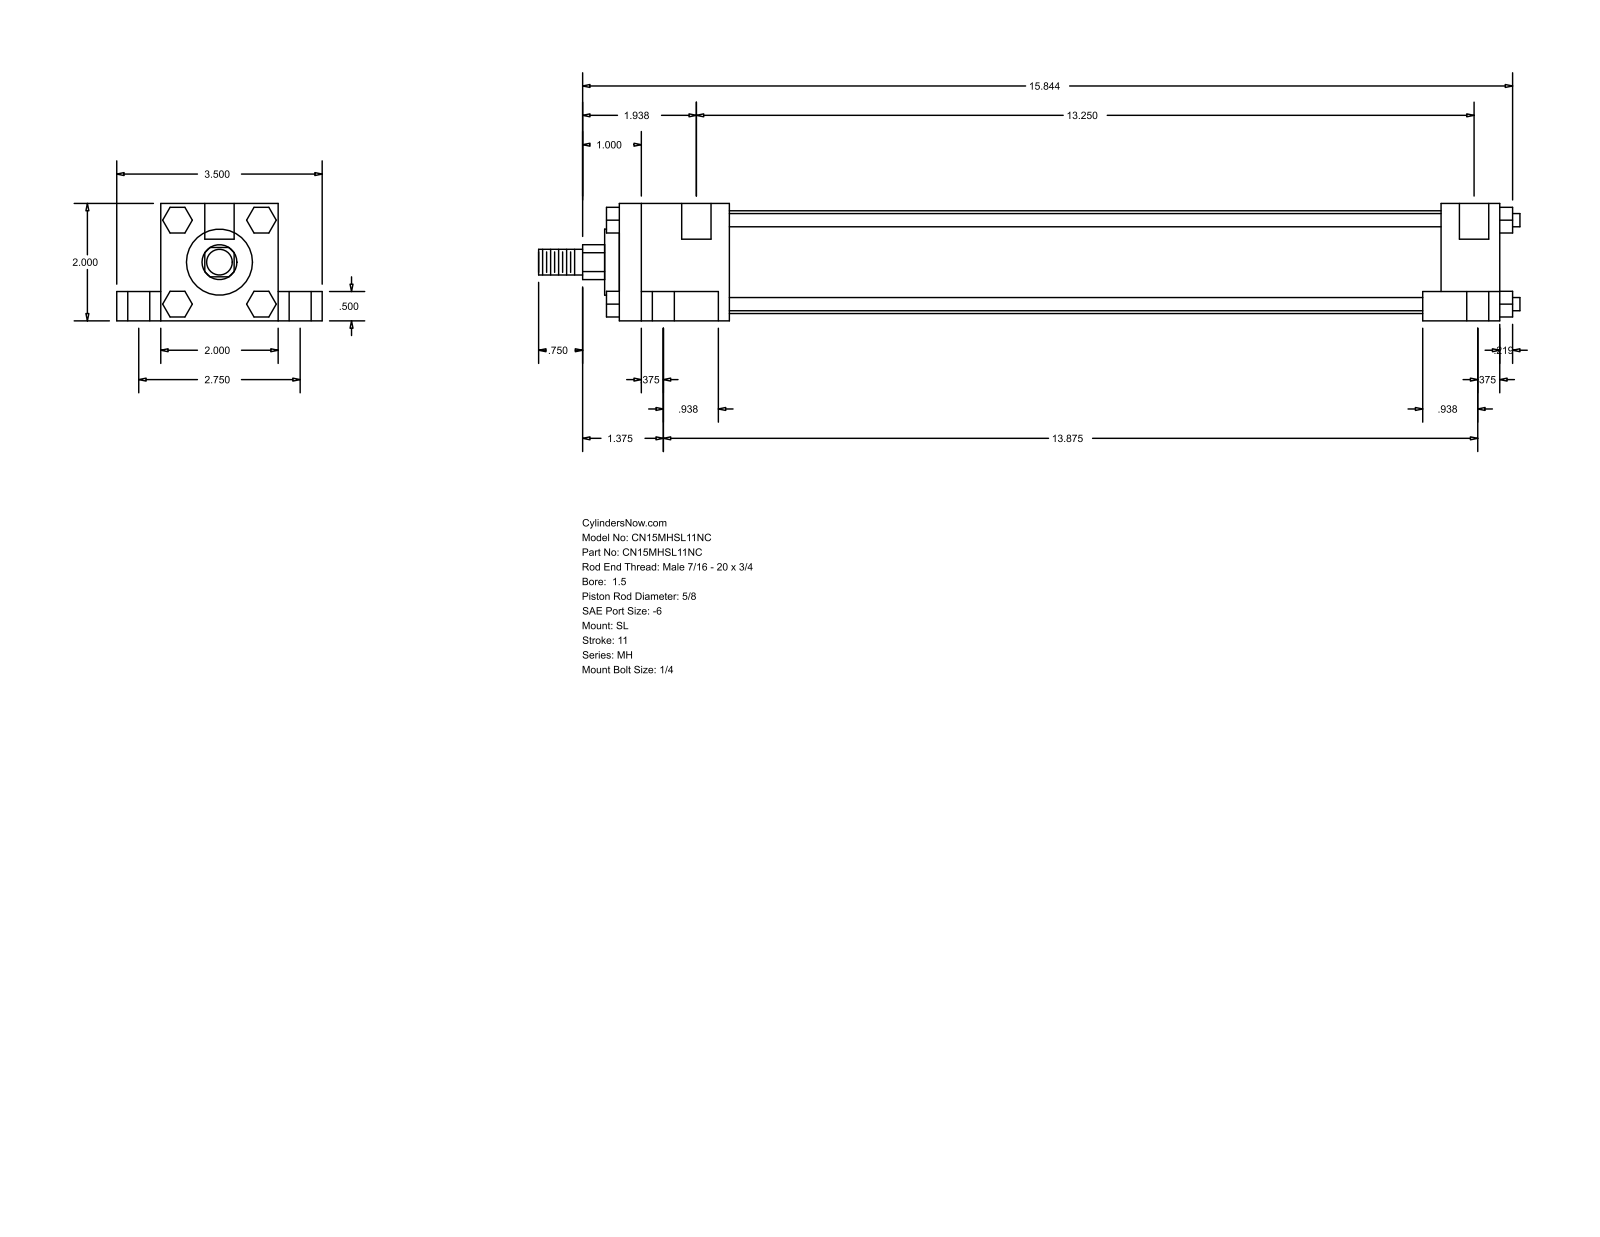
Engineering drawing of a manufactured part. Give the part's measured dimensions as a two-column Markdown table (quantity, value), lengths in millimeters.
| quantity | value |
| --- | --- |
| part name | MH_SL__0150_0.625 |
| STEP written by | GSSL Pune (CONFIG_CONTROL_DESIGN) |
| units | millimeters |
| bodies | 0 solids, 148 faces (112 planar, 36 cylindrical, 0 other) |
| overall size | 424.66 × 88.9 × 50.8 |
| round holes (diameter × count) | 5.56 × 4, 9.53 × 4, 15.88 × 4, 12.7 × 2 |
| round bosses / shafts (diameter × count) | 5.71 × 4, 44.45 × 1, 28.57 × 1, 15.88 × 1, 11.11 × 1 |
| partial cylindrical surfaces (radius × count) | 7.54 × 1 |
| main face-to-face distances | 50.8, 38.1, 19.05, 12.7, 69.85, 381, 25.4, 9.52, 33.34, 338.14 |
| hole center spacings | 34.96, 36.65, 37.73, 69.84, 339.72, 339.94, 343.09, 352.43 |
